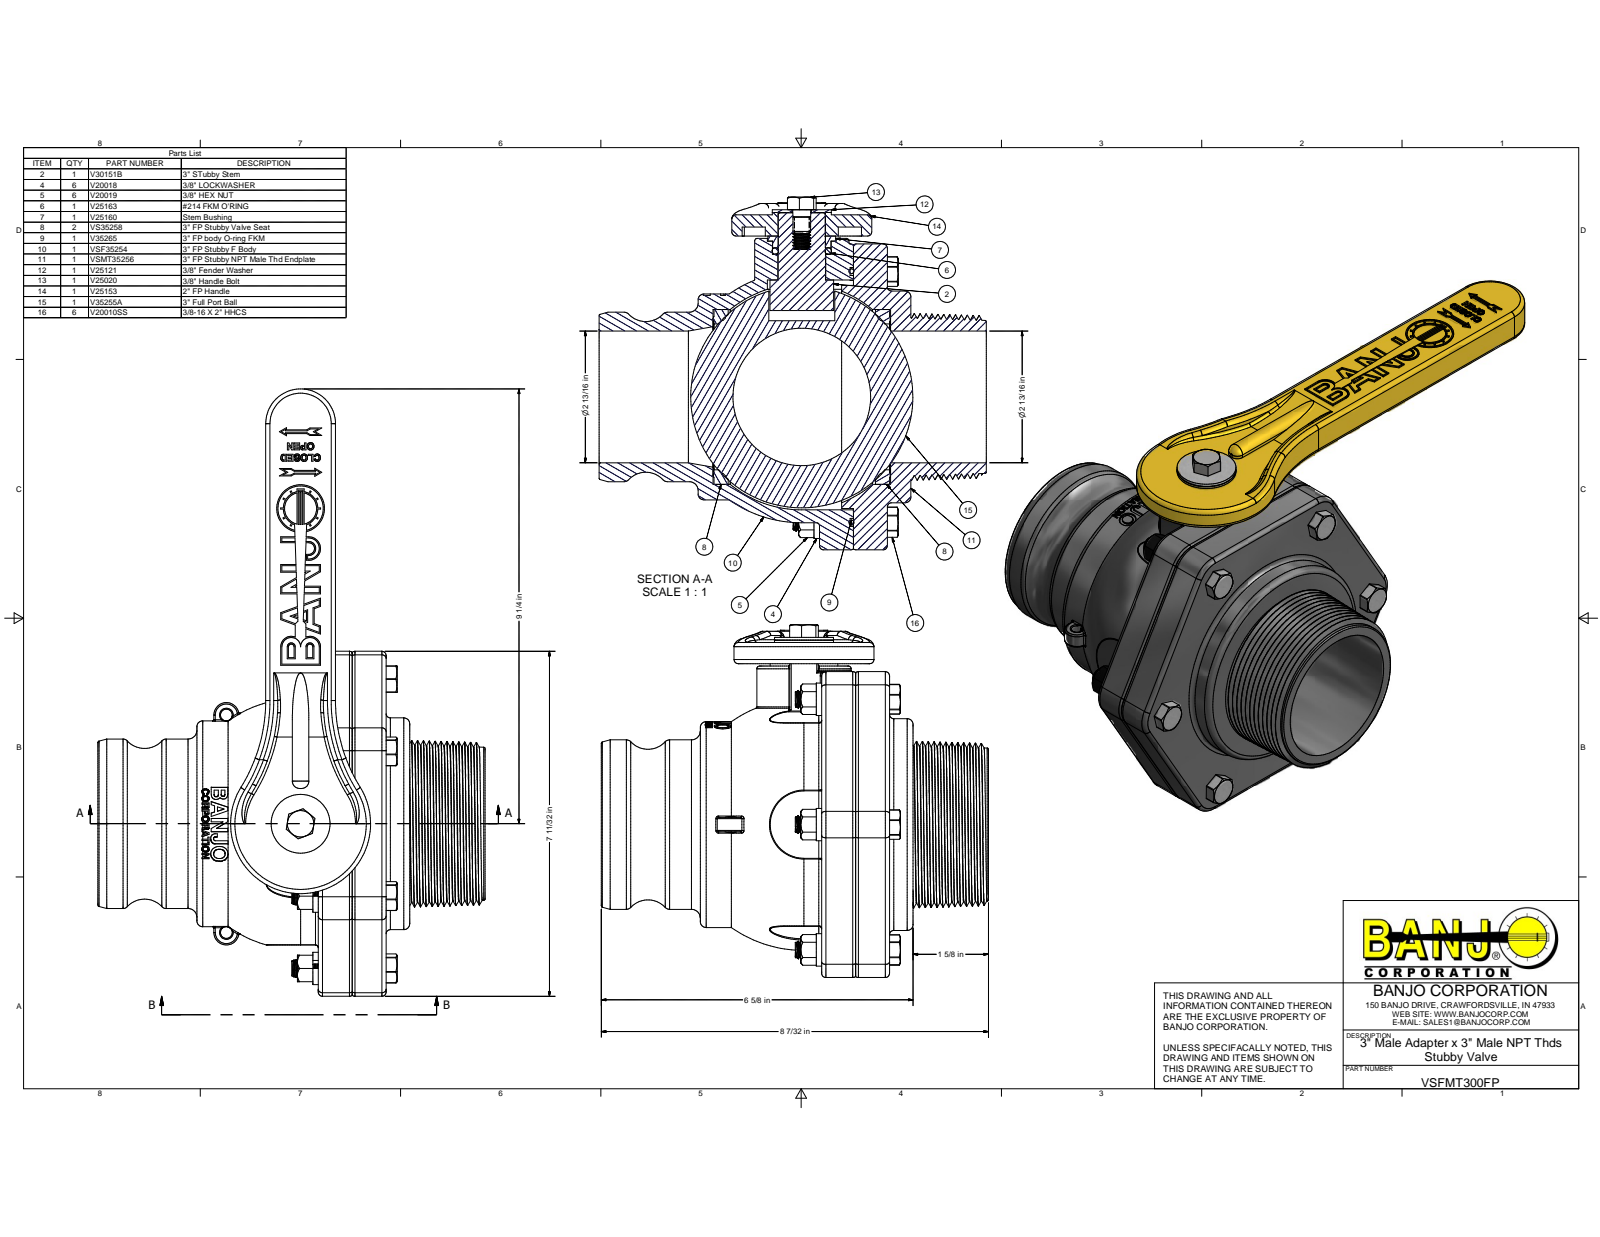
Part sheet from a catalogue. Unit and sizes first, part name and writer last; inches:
Units: inches
Overall size (bounding box): 12.906 × 8.215 × 7.497
Round holes (diameter × count): ⌀0.307 ×7, ⌀0.385 ×6, ⌀0.44 ×6, ⌀0.375 ×3, ⌀0.25 ×2, ⌀0.406 ×1, ⌀0.681 ×1, ⌀0.962 ×1, ⌀1 ×1, ⌀1.016 ×1, ⌀1.245 ×1, ⌀1.46 ×1
Round bosses / shafts (diameter × count): ⌀0.324 ×90, ⌀0.375 ×7, ⌀0.687 ×6, ⌀5.16 ×1, ⌀4.74 ×1, ⌀4.5 ×1, ⌀4.375 ×1, ⌀3.715 ×1
Partial cylindrical surfaces — rounded edges, fillets, slot ends (radius × count): R0.03 ×33, R0.09 ×32, R0.162 ×12, R0.06 ×10, R0.032 ×6, R0.32 ×6, R0.563 ×6, R0.5 ×4
Main face-to-face distances: 0.72, 1.44, 6.5, 0.5, 1.22, 0.3, 1.145, 2.625, 0.79, 0.26
Hole centre spacings: 3.075, 3.075, 5.326, 2.796, 6.15, 5.326, 6.699, 4.62
Volume: 98.68 in³ · Surface area: 583.3 in²
Bodies: 30 solids, 2571 faces (691 planar, 827 cylindrical, 1053 other)
Part name (STEP PRODUCT): VSF35254X; VSF35254; VSMT35256X; VSMT35256 (+8 more)
STEP written by: Autodesk Inventor 2014 (AUTOMOTIVE_DESIGN)
